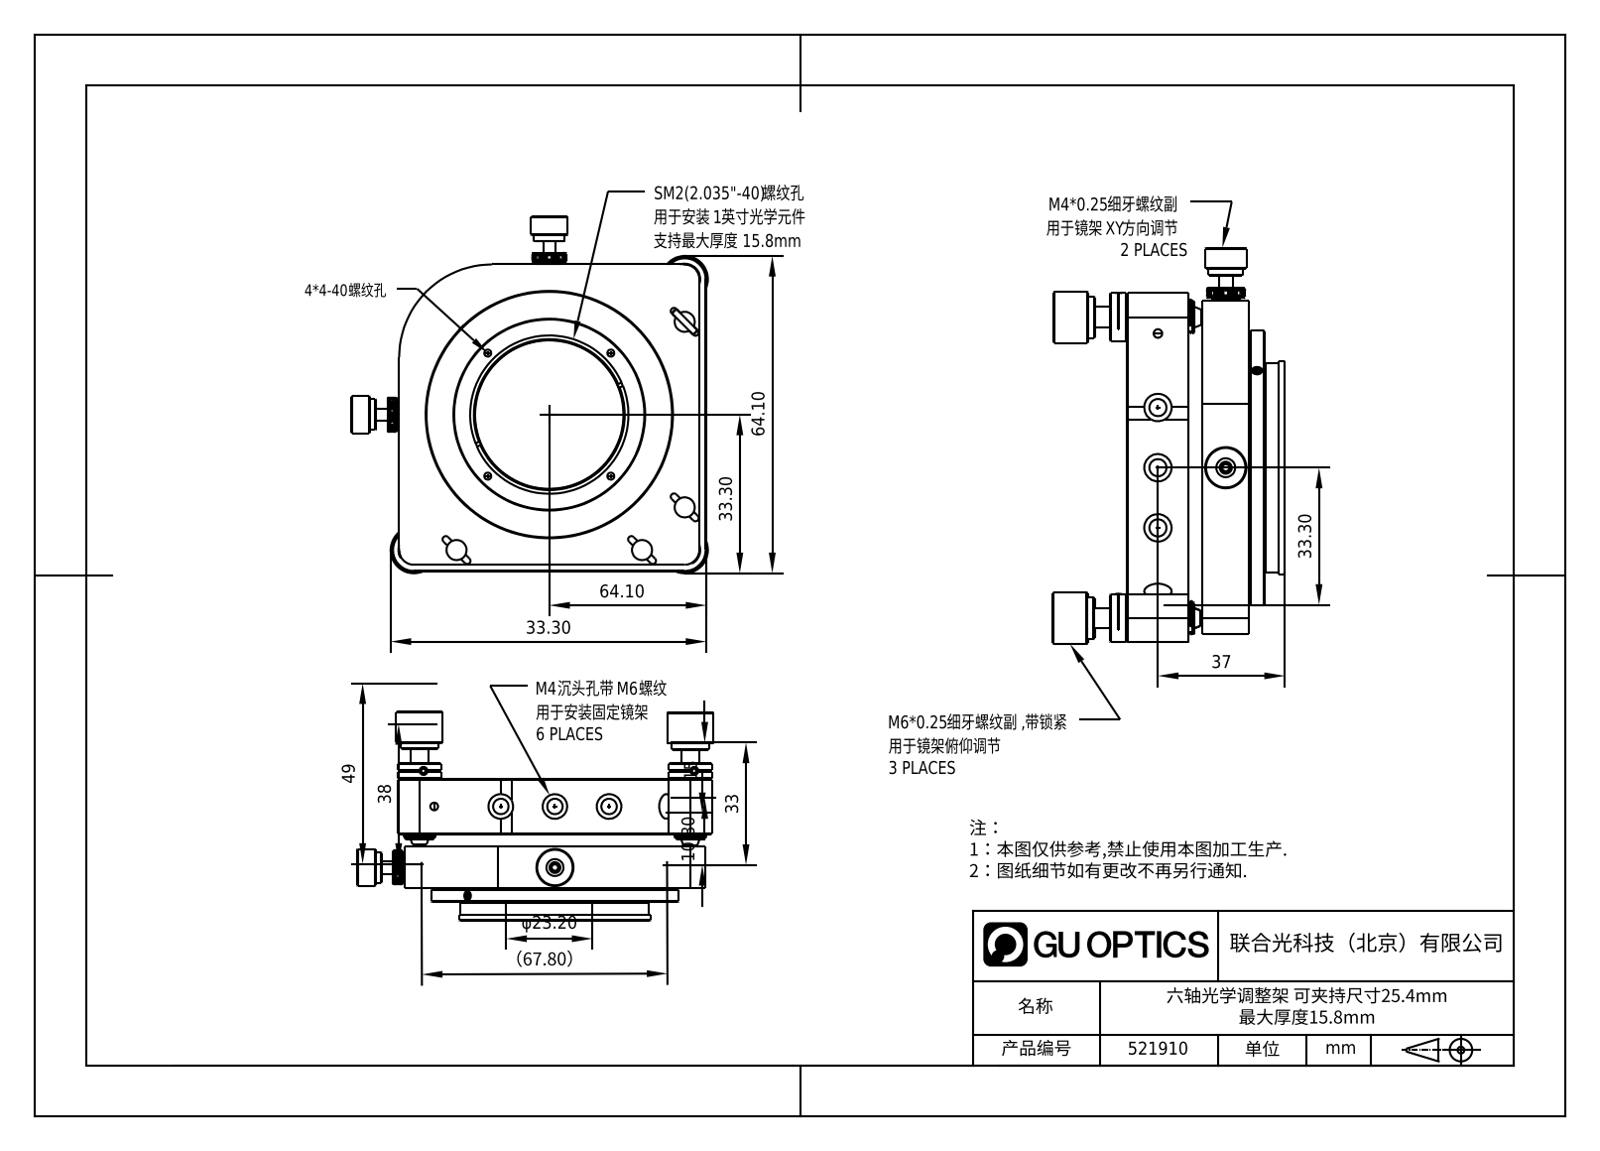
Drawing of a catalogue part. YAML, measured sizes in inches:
part_name: "521910"
step_written_by: "SolidWorks 2020 (CONFIG_CONTROL_DESIGN)"
units: inches
bodies: {solids: 0, faces: 922, planar: 446, cylindrical: 261, other: 215}
overall_size: [4.539, 4.539, 2.665]
round_holes:
  - {diameter: 0.197, count: 6}
  - {diameter: 0.315, count: 6}
  - {diameter: 0.189, count: 5}
  - {diameter: 0.081, count: 4}
  - {diameter: 0.114, count: 4}
  - {diameter: 0.256, count: 4}
  - {diameter: 0.098, count: 3}
  - {diameter: 0.374, count: 3}
  - {diameter: 0.138, count: 2}
  - {diameter: 2.362, count: 1}
  - {diameter: 2.441, count: 1}
  - {diameter: 3.15, count: 1}
round_bosses_or_shafts:
  - {diameter: 0.089, count: 4}
  - {diameter: 0.591, count: 3}
  - {diameter: 0.551, count: 3}
  - {diameter: 0.236, count: 3}
  - {diameter: 0.472, count: 2}
  - {diameter: 0.394, count: 2}
  - {diameter: 0.315, count: 2}
  - {diameter: 0.157, count: 2}
partial_cylinders:
  - {radius: 0.041, count: 16}
  - {radius: 0.197, count: 3}
  - {radius: 0.008, count: 2}
  - {radius: 0.079, count: 2}
  - {radius: 0.217, count: 2}
  - {radius: 0.394, count: 2}
  - {radius: 1.102, count: 2}
  - {radius: 0.177, count: 1}
face_to_face_distances: [0.866, 0.531, 0.709, 0.079, 0.453, 0.236, 0.945, 0.089, 1.398, 0.157]
hole_center_spacings: [0.543, 0.689, 1.039, 2.09, 2.906, 0.848, 1.537, 1.723]
